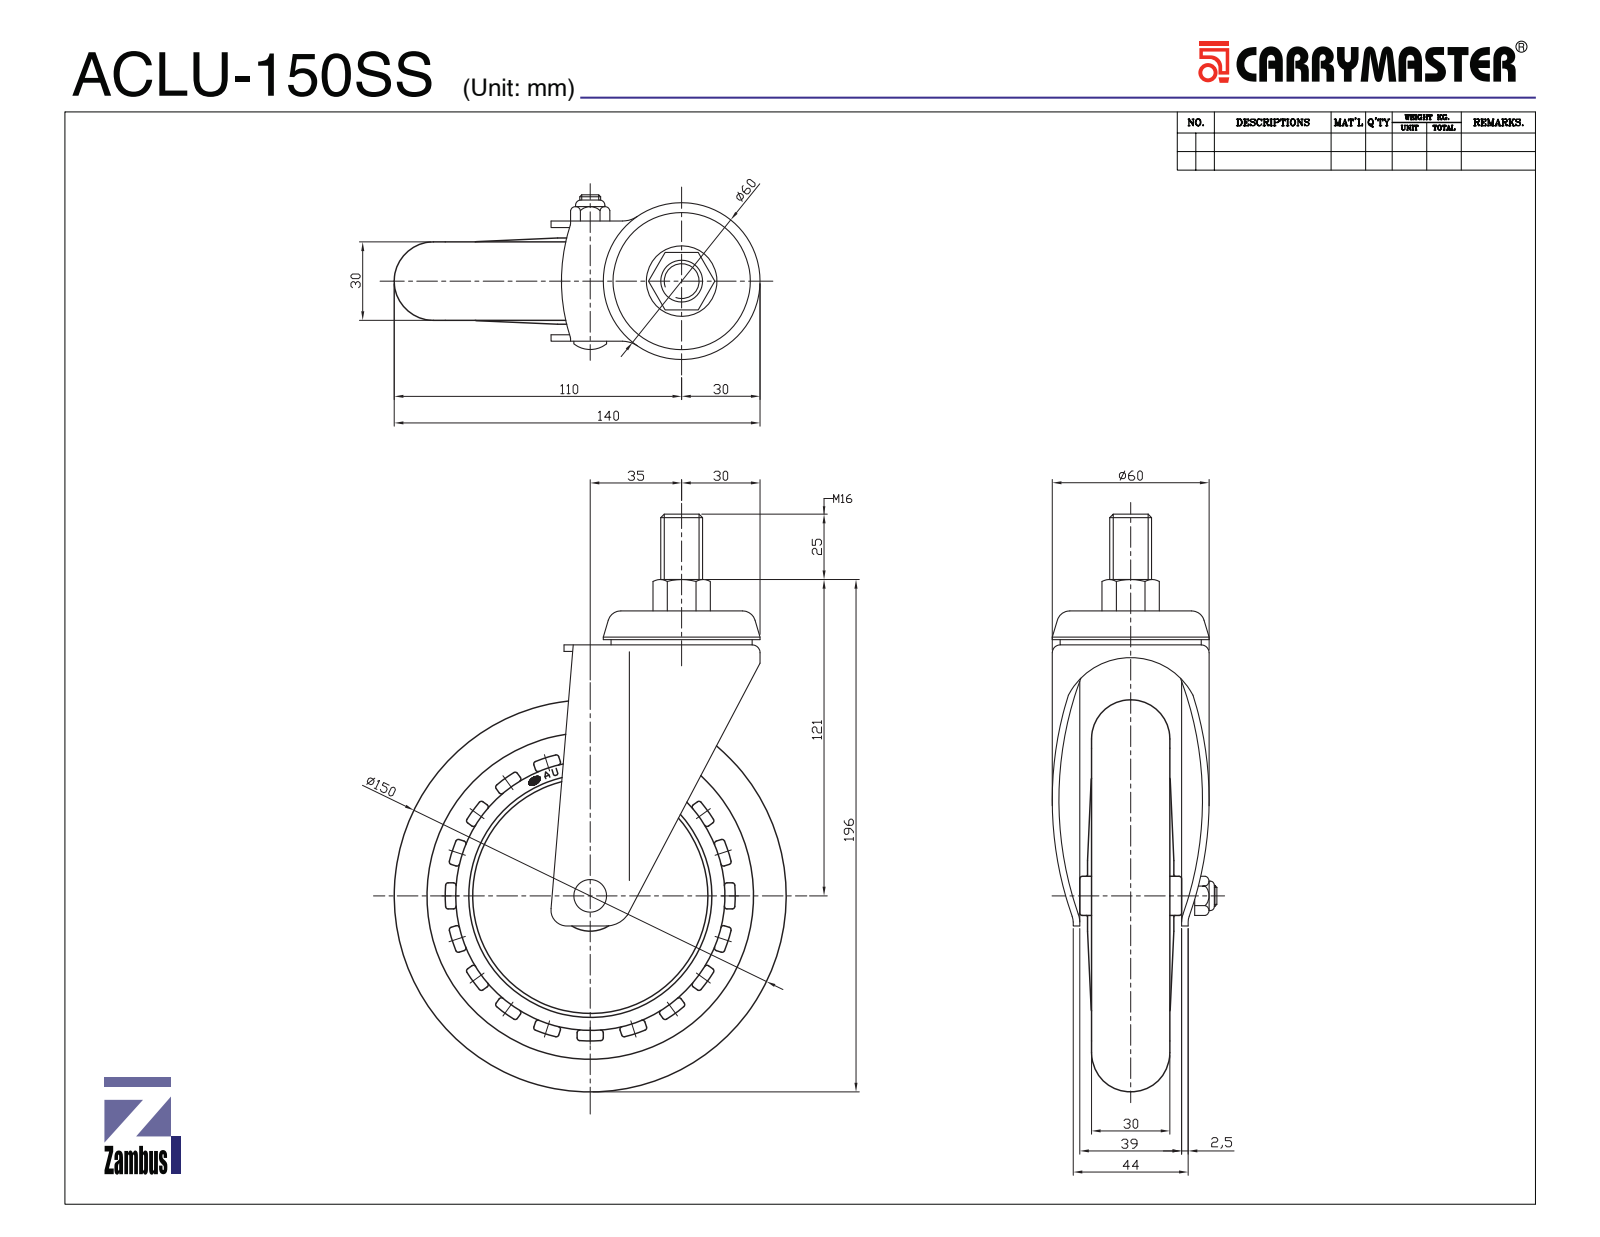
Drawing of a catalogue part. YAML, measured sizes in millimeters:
part_name: "ACLU-150SS"
step_written_by: "SolidWorks 2015 (CONFIG_CONTROL_DESIGN)"
units: millimeters
bodies: {solids: 14, faces: 992, planar: 450, cylindrical: 281, other: 261}
overall_size: [220.93, 150, 61.4]
volume: 450901
surface_area: 173345
round_holes:
  - {diameter: 6.8, count: 1}
  - {diameter: 8, count: 1}
  - {diameter: 9.6, count: 1}
  - {diameter: 12.6, count: 1}
  - {diameter: 19.6, count: 1}
  - {diameter: 22, count: 1}
  - {diameter: 28.62, count: 1}
  - {diameter: 29.82, count: 1}
  - {diameter: 39.2, count: 1}
  - {diameter: 88, count: 1}
  - {diameter: 92, count: 1}
  - {diameter: 103, count: 1}
round_bosses_or_shafts:
  - {diameter: 16, count: 2}
  - {diameter: 120, count: 1}
  - {diameter: 90, count: 1}
  - {diameter: 59.7, count: 1}
  - {diameter: 40, count: 1}
  - {diameter: 32, count: 1}
  - {diameter: 21.5, count: 1}
  - {diameter: 20, count: 1}
partial_cylinders:
  - {radius: 1, count: 88}
  - {radius: 3.86, count: 19}
  - {radius: 46.25, count: 16}
  - {radius: 1.5, count: 2}
  - {radius: 2.5, count: 2}
  - {radius: 7, count: 2}
  - {radius: 10, count: 2}
  - {radius: 12.5, count: 2}
face_to_face_distances: [30.5, 12.3, 18.7, 11.8, 0.5, 18.2, 2.5, 5, 31, 5.5]
